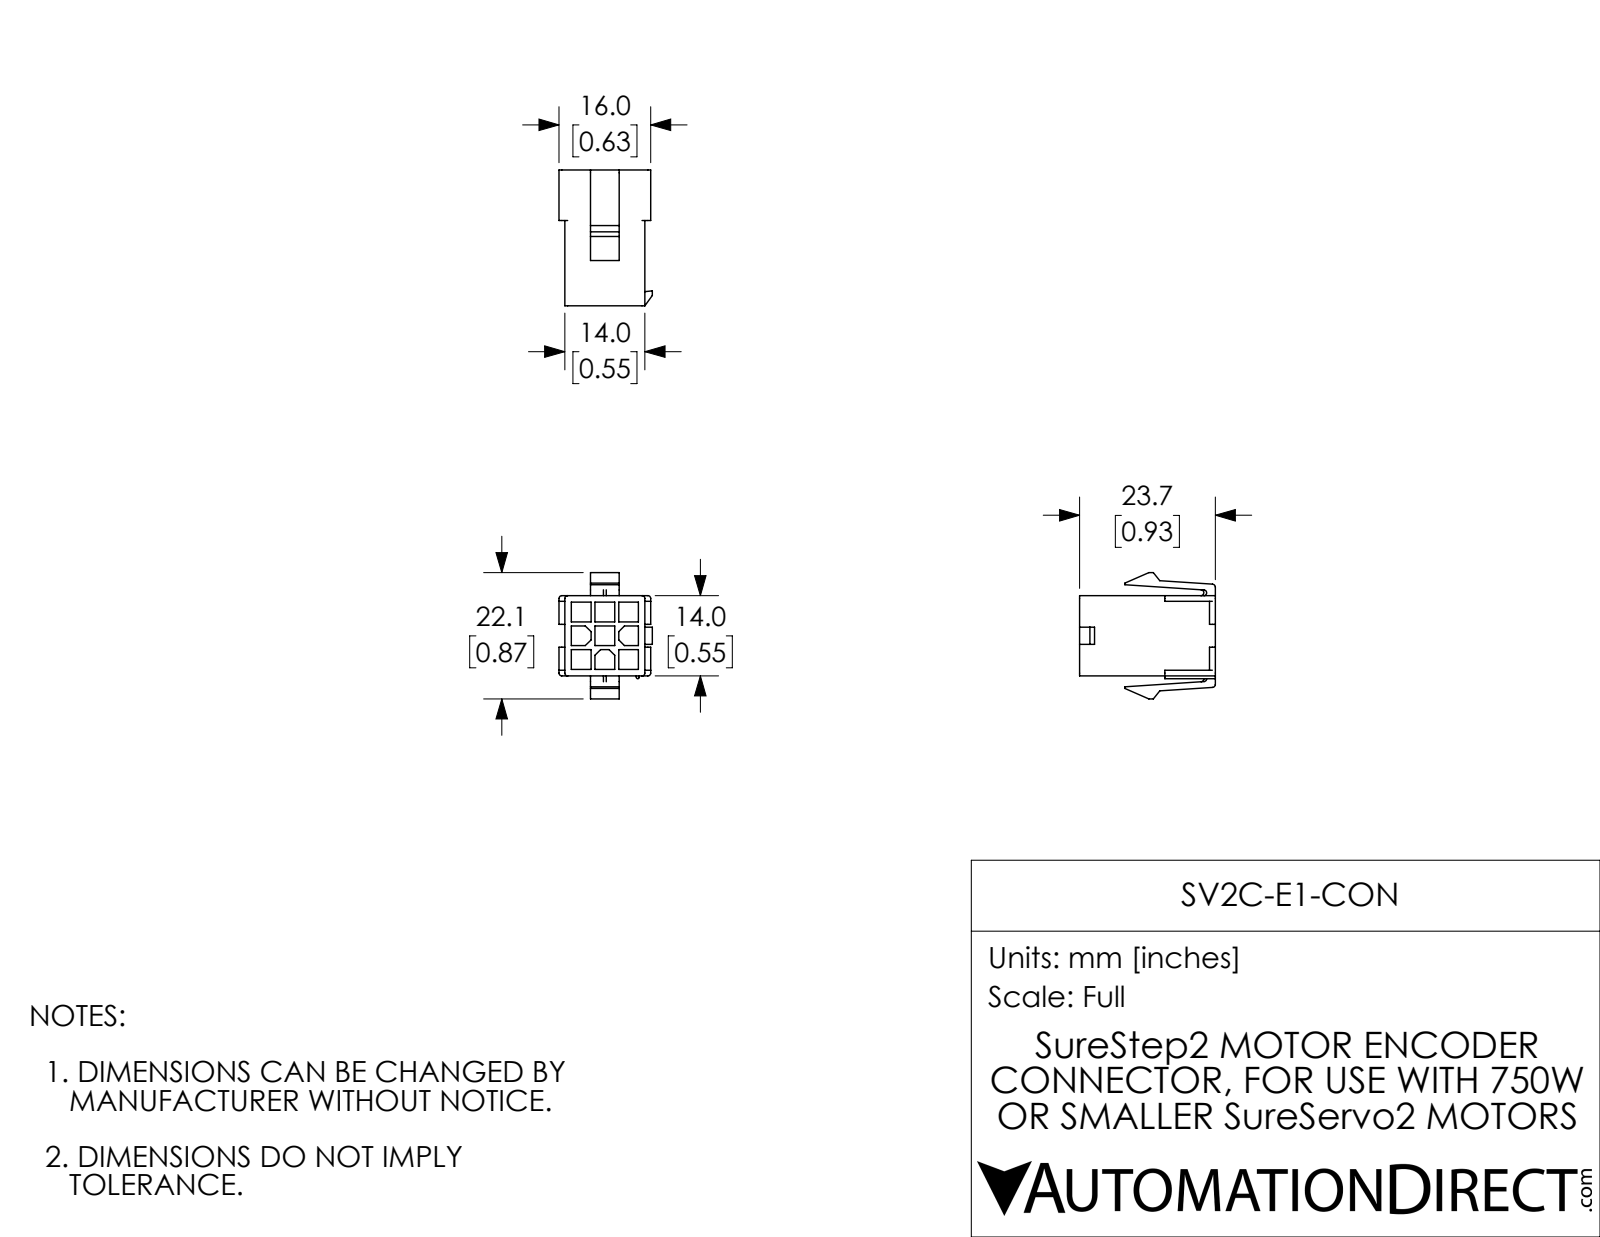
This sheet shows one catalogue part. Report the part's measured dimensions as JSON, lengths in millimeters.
{"part_name": "SV2C-E1-CON", "step_written_by": "SolidWorks 2017 (AUTOMOTIVE_DESIGN)", "units": "millimeters", "bodies": {"solids": 1, "faces": 349, "planar": 322, "cylindrical": 27, "other": 0}, "overall_size": [23.7, 22.1, 16.3], "volume_mm3": 4690, "surface_area_mm2": 2479, "partial_cylinders_radius": [[0.5, 14], [0.5, 2], [0.3, 1]], "face_to_face_distances": [14, 1, 22.7, 21.7, 4.1, 1.1, 23.7, 4.5, 9.5, 3.6]}
